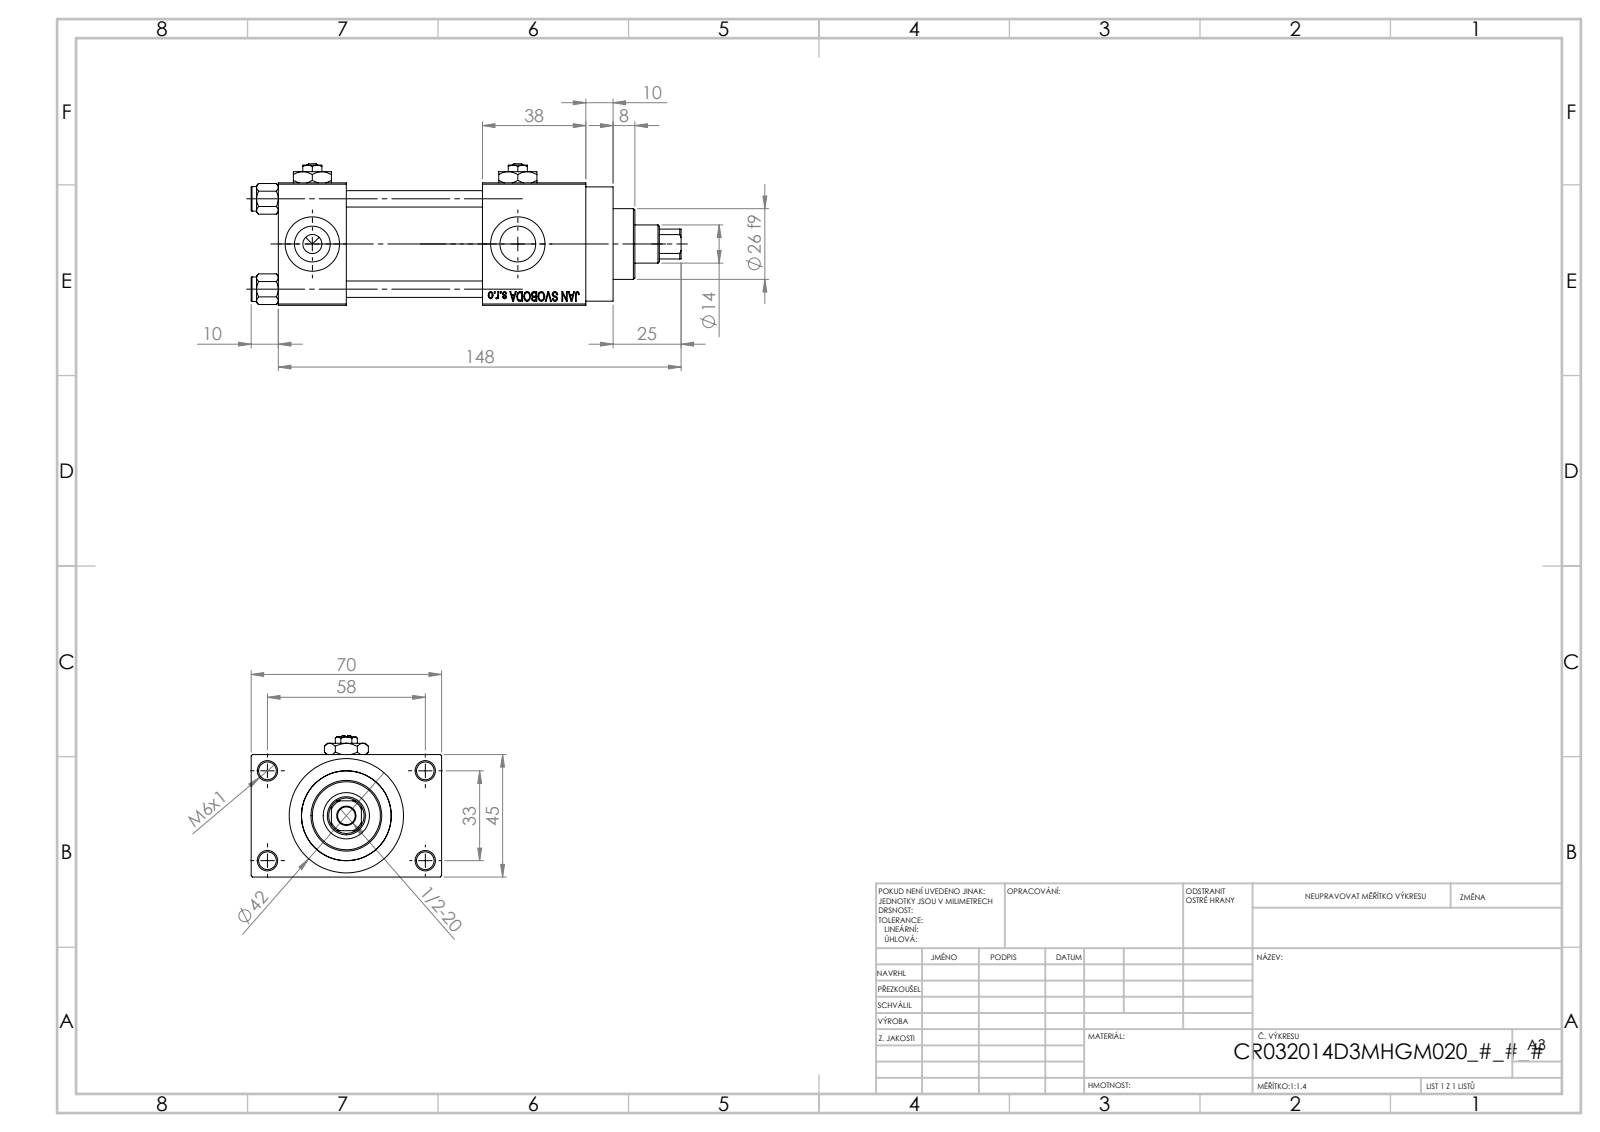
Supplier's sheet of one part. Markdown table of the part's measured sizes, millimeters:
| quantity | value |
| --- | --- |
| part name | V215_VC_A; V215CR_VCP_D; NUT_M5_D; V215CR_D_TYCINKA (+2 more) |
| STEP written by | SolidWorks 2019 (CONFIG_CONTROL_DESIGN) |
| units | millimeters |
| bodies | 13 solids, 1201 faces (542 planar, 99 cylindrical, 560 other) |
| overall size | 158 × 70 × 52 |
| volume | 229 076 mm³ |
| surface area | 77 129 mm² |
| round holes (diameter × count) | 6.5 × 5, 6 × 4, 13.16 × 4, 20 × 4, 7 × 3, 14 × 1, 17 × 1, 24 × 1, 32 × 1, 33 × 1 |
| round bosses / shafts (diameter × count) | 9 × 4, 42 × 1, 38 × 1, 26 × 1 |
| partial cylindrical surfaces (radius × count) | 6.5 × 1 |
| main face-to-face distances | 45, 25, 50, 12.5, 75, 57.5, 88, 38, 113, 70 |
| hole center spacings | 12.4, 23.48, 33.2, 33.37, 35.35, 45.6, 56.35, 33 |
